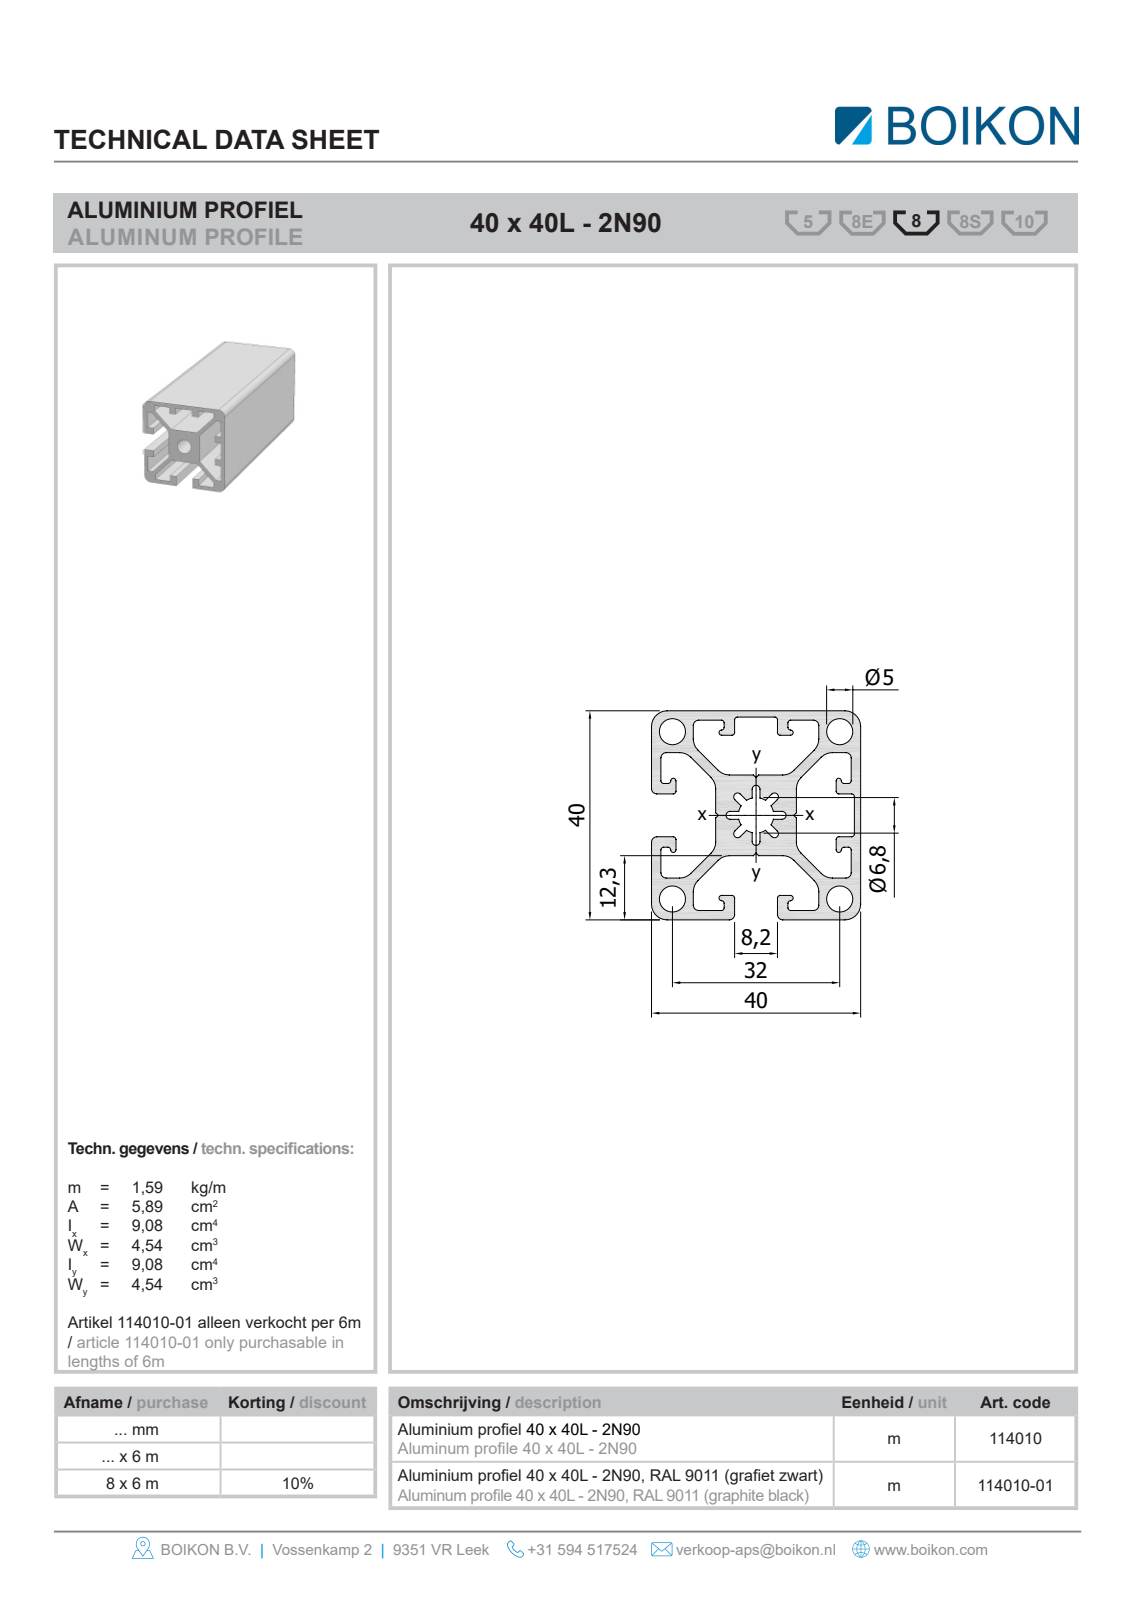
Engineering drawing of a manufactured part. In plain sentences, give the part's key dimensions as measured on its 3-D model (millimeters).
The part is named "Root; 11401040x40L-2N90BOIKON0". Its 3-D file was written by "HiCAD 2013 1802.4 Build 509 (AUTOMOTIVE_DESIGN)". It is 1 solid with 67 faces: 62 planar, 5 cylindrical and 0 other. Overall it measures 1000 by 40 by 40 millimeters. Its volume is 633 616 cubic millimeters and its surface area 476 780 square millimeters. Round holes: 1 of diameter 6.8. Partial cylindrical surfaces (rounded edges, fillets, slot ends): 4 of radius 3. The main face-to-face distances are 1.8, 38.2, 40, 12.4, 27.6, 10.6, 25.8, 11.2, 8.2, 15.9.
